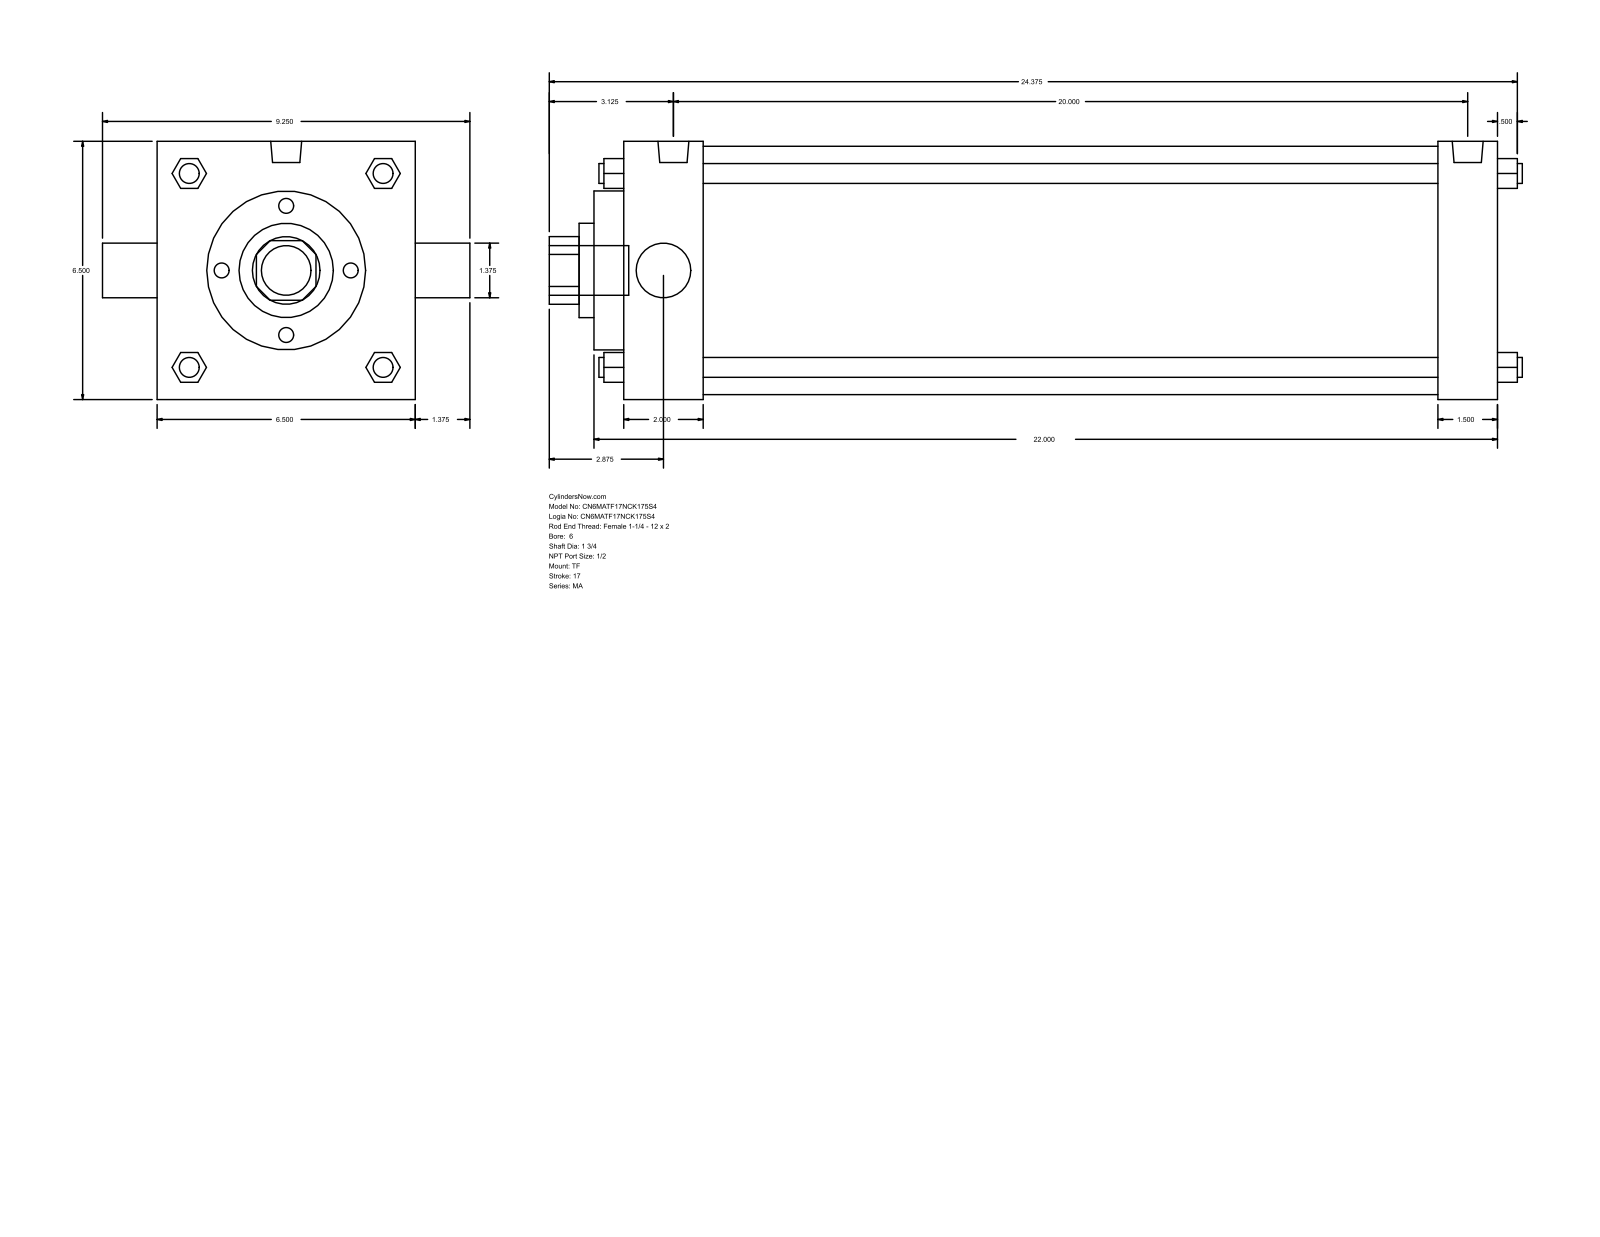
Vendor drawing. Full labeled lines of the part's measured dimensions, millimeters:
Part name (STEP PRODUCT): MA_TF__0600_1.75
STEP written by: GSSL Pune (CONFIG_CONTROL_DESIGN)
Units: millimetres
Bodies: 0 solids, 122 faces (93 planar, 29 cylindrical, 0 other)
Overall size (bounding box): 622.3 × 234.95 × 165.1
Round holes (diameter × count): ⌀34.92 ×1, ⌀44.45 ×1, ⌀60.33 ×1, ⌀101.6 ×1, ⌀158.75 ×1
Round bosses / shafts (diameter × count): ⌀12.7 ×4, ⌀17.46 ×3, ⌀19.77 ×2, ⌀31.75 ×1
Partial cylindrical surfaces — rounded edges, fillets, slot ends (radius × count): R21.63 ×1
Main face-to-face distances: 165.1, 558.8, 19.05, 50.8, 508, 520.71, 469.91, 38.09, 69.85, 539.76
